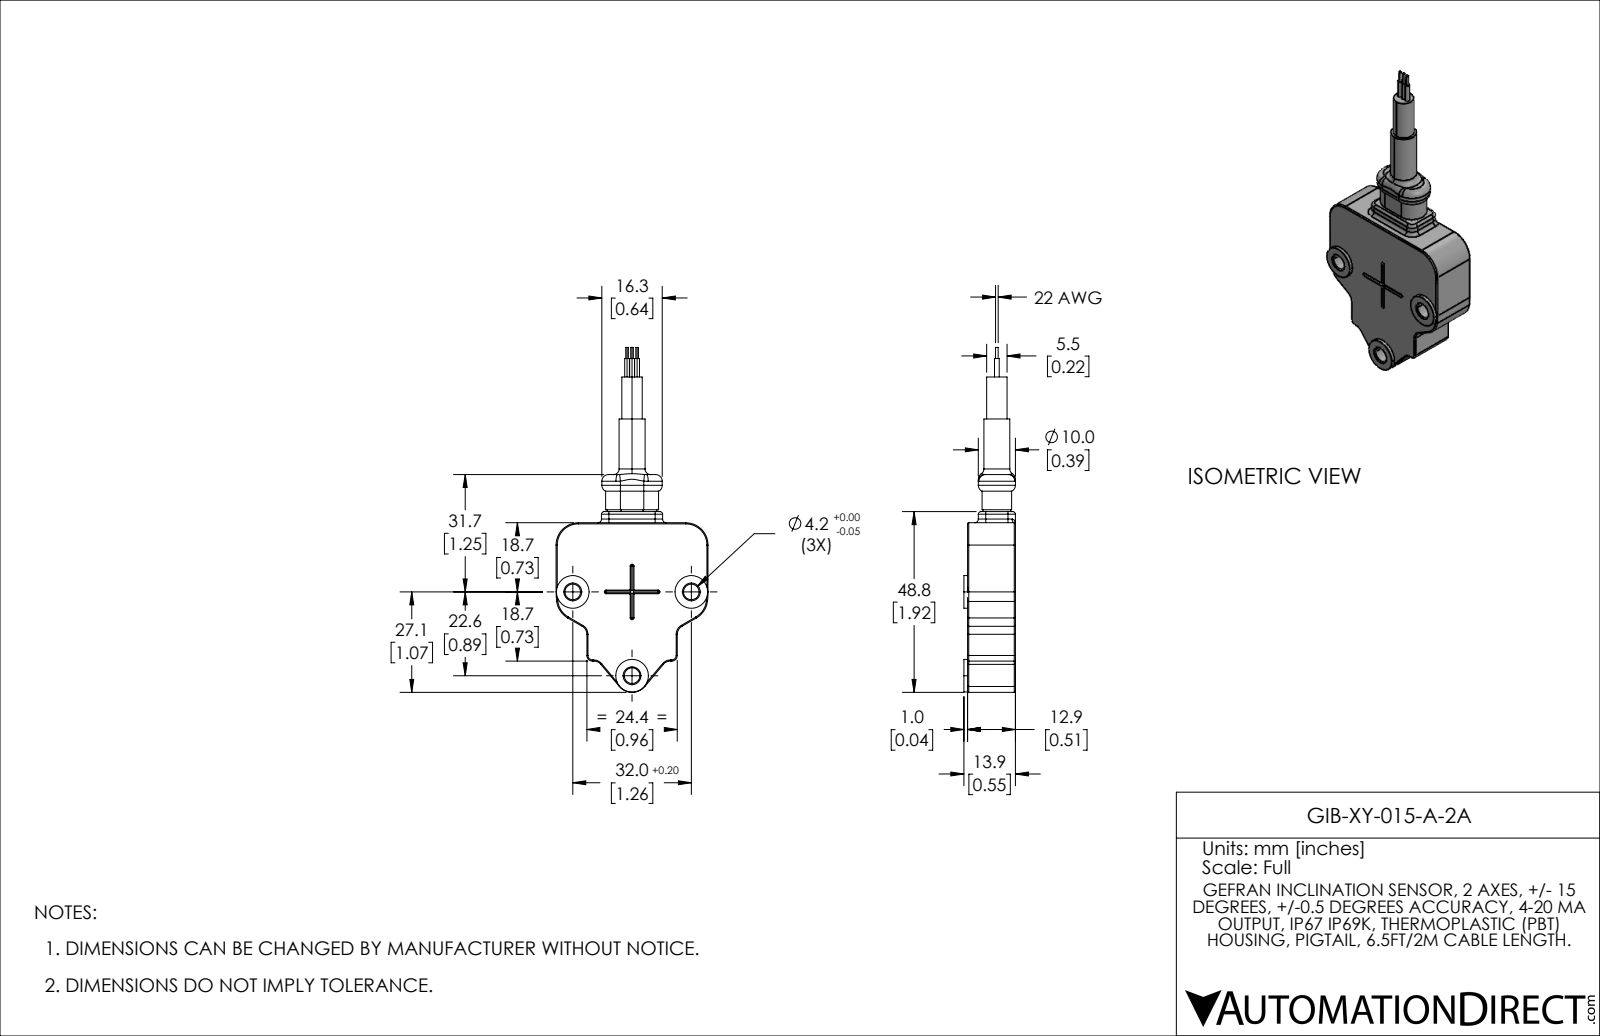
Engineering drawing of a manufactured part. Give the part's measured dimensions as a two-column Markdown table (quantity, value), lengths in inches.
| quantity | value |
| --- | --- |
| part name | GIB-XY-015-A-2A |
| STEP written by | SolidWorks 2021 (AUTOMOTIVE_DESIGN) |
| units | inches |
| bodies | 1 solid, 201 faces (47 planar, 87 cylindrical, 67 other) |
| overall size | 3.663 × 1.614 × 0.547 |
| volume | 1.246 in³ |
| surface area | 9.975 in² |
| round holes (diameter × count) | 0.165 × 3 |
| round bosses / shafts (diameter × count) | 0.346 × 3, 0.051 × 3, 0.028 × 3, 0.276 × 1, 0.217 × 1 |
| partial cylindrical surfaces (radius × count) | 0.012 × 20, 0.008 × 4, 0.028 × 4, 0.079 × 4, 0.098 × 4, 0.236 × 4, 0.039 × 3, 0.059 × 2 |
| main face-to-face distances | 0.508, 0.039, 1.614, 0.327, 1.287, 0.547, 0.961, 0.354, 0.154, 0.118 |
| hole center spacings | 1.09, 1.26 |
